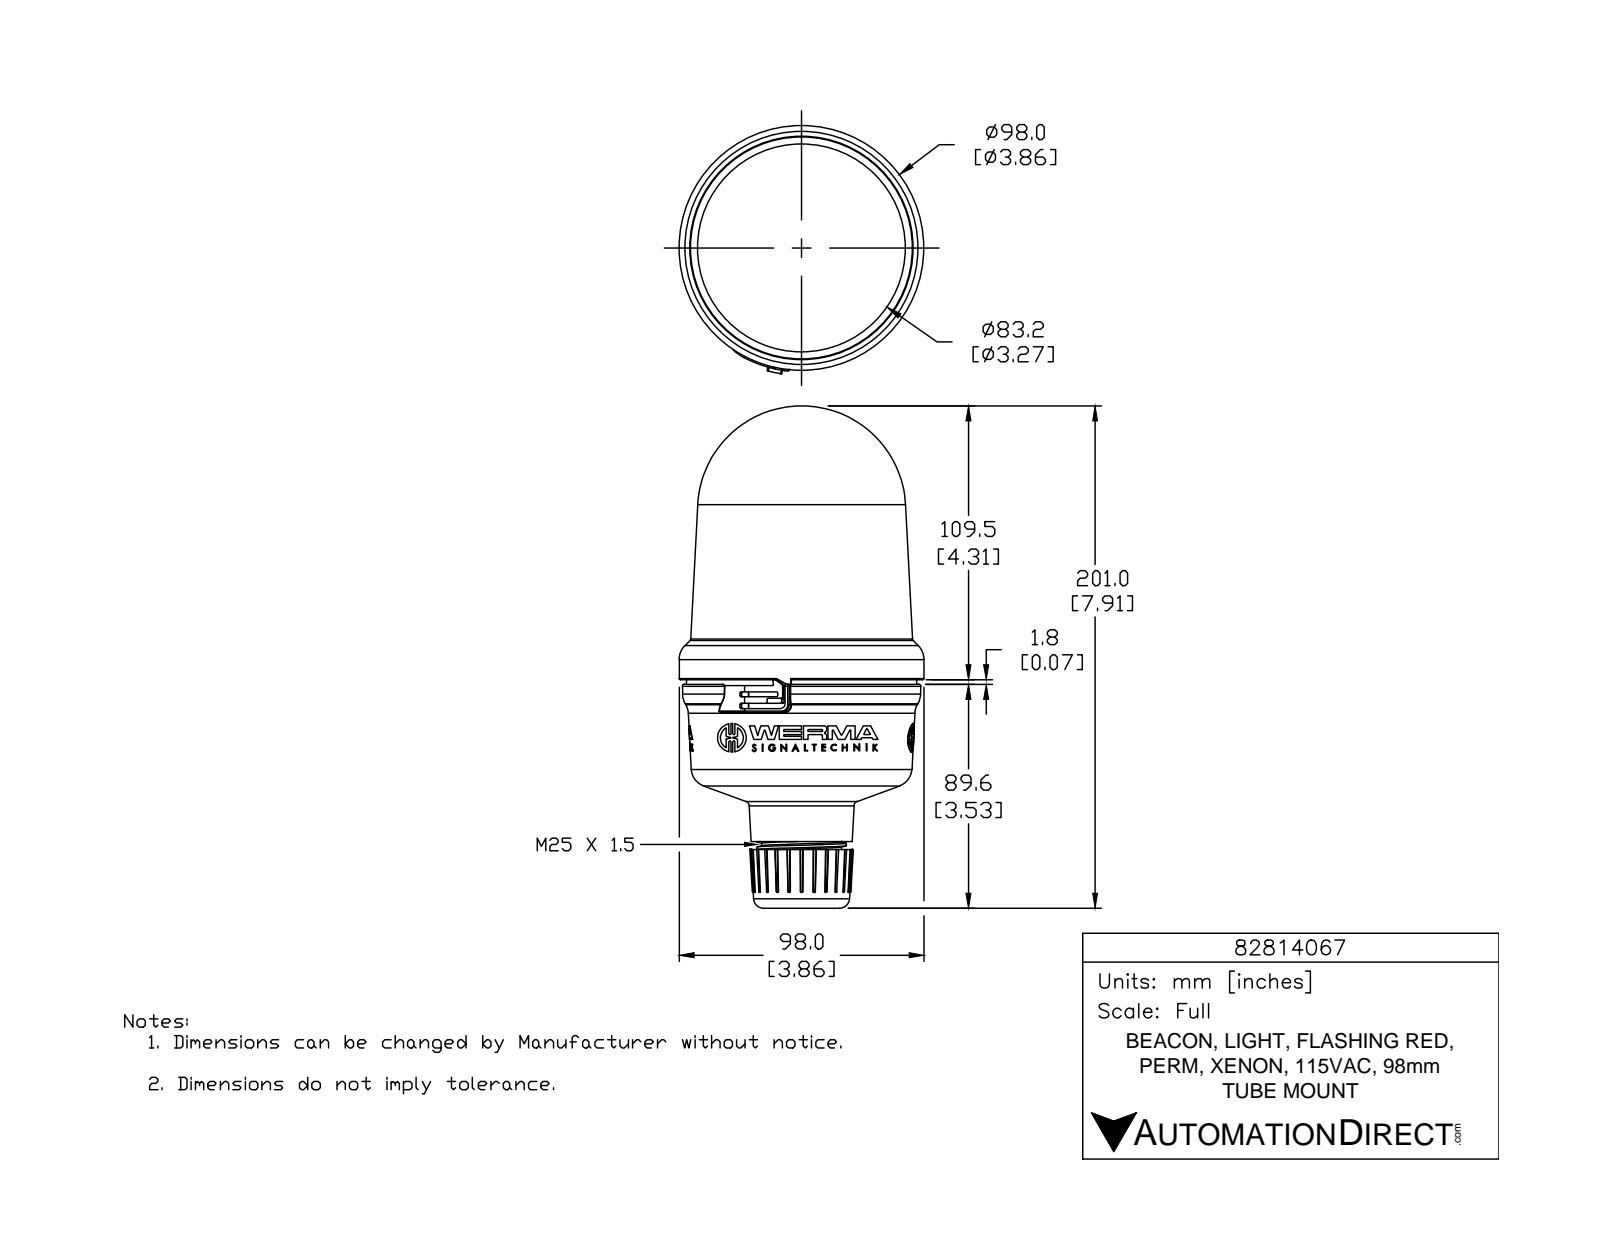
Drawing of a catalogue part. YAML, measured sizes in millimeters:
part_name: "82814067"
step_written_by: "SolidWorks 2015 (AUTOMOTIVE_DESIGN)"
units: millimeters
bodies: {solids: 1, faces: 1006, planar: 554, cylindrical: 189, other: 263}
overall_size: [201, 99.4, 98]
volume: 896400
surface_area: 58960
round_holes:
  - {diameter: 2, count: 3}
  - {diameter: 25.7, count: 1}
  - {diameter: 26, count: 1}
round_bosses_or_shafts:
  - {diameter: 11.5, count: 3}
  - {diameter: 2.9, count: 3}
  - {diameter: 98, count: 1}
  - {diameter: 35.8, count: 1}
  - {diameter: 32, count: 1}
partial_cylinders:
  - {radius: 0.5, count: 12}
  - {radius: 0.2, count: 9}
  - {radius: 0.2, count: 6}
  - {radius: 0.4, count: 6}
  - {radius: 0.4, count: 6}
  - {radius: 0.4, count: 6}
  - {radius: 6.7, count: 6}
  - {radius: 0.2, count: 3}
face_to_face_distances: [56.2, 11.7, 68, 8.5, 3.2, 64.7, 66.1, 62.9, 54.4, 1.9]
